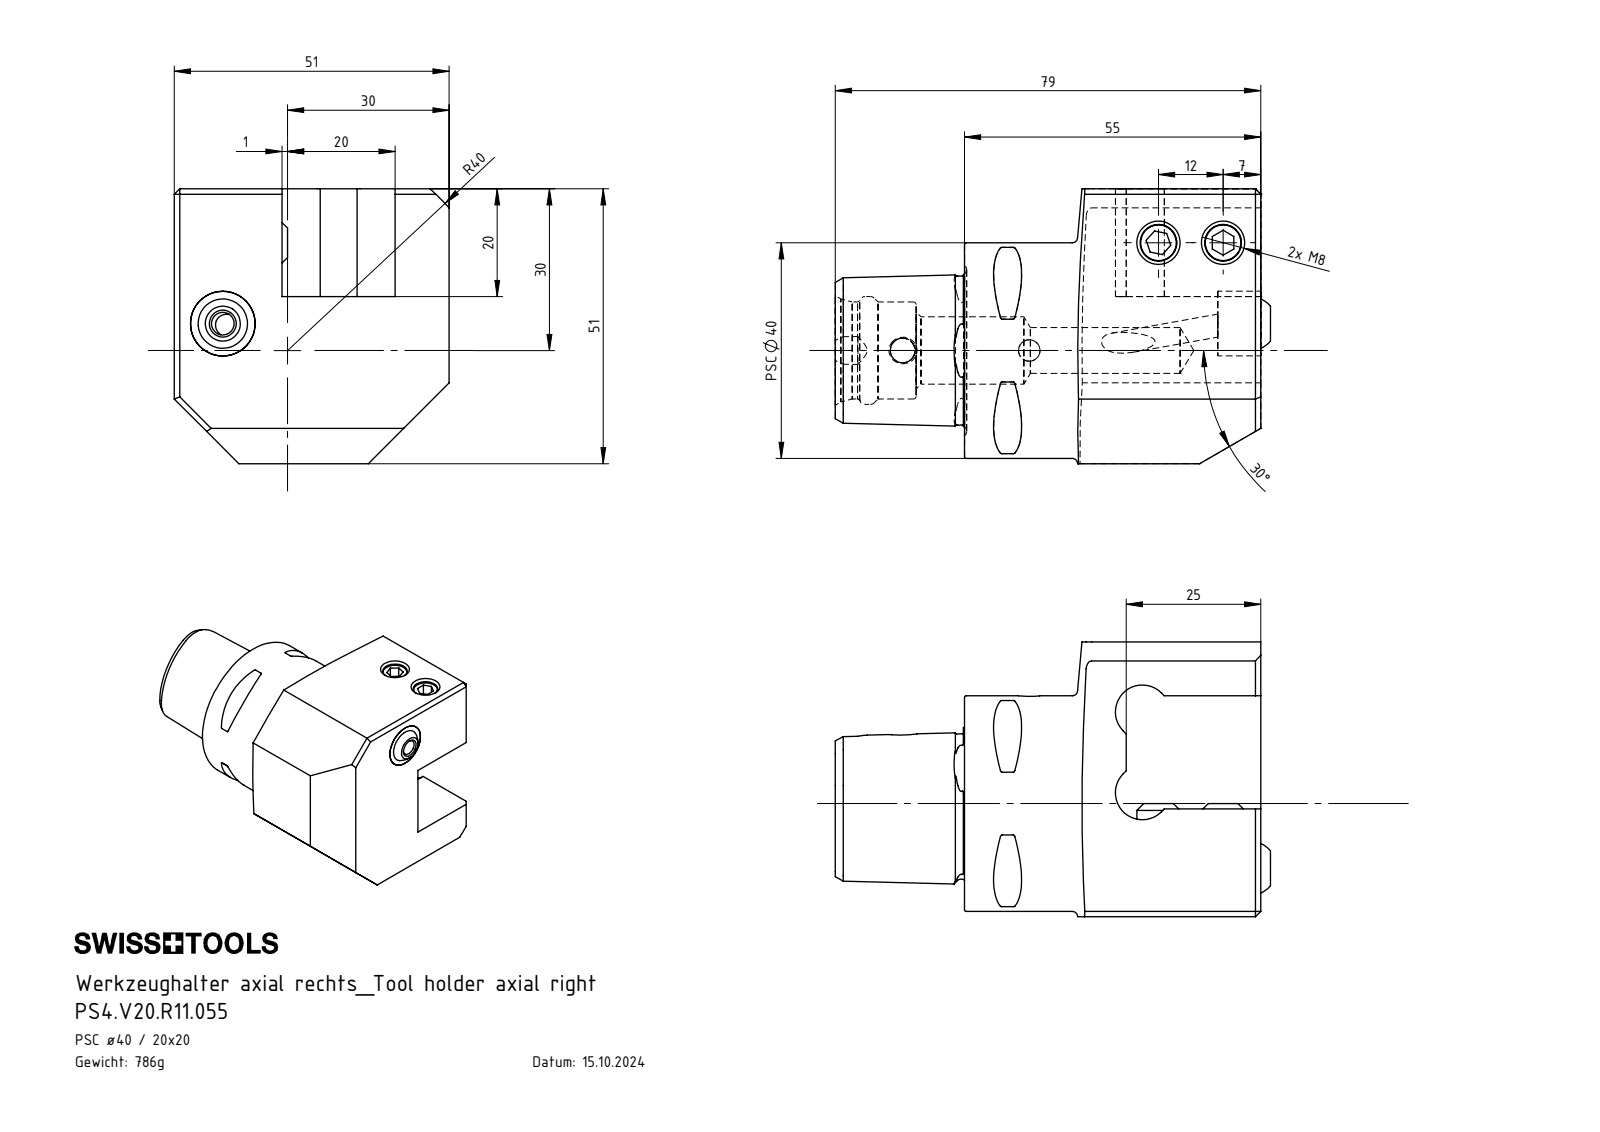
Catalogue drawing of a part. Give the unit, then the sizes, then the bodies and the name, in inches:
Units: inches
Overall size (bounding box): 3.181 × 2.008 × 2.008
Round holes (diameter × count): ⌀0.165 ×2, ⌀0.268 ×2, ⌀0.157 ×1, ⌀0.181 ×1, ⌀0.276 ×1, ⌀0.335 ×1, ⌀0.472 ×1, ⌀0.492 ×1, ⌀0.709 ×1, ⌀0.787 ×1
Round bosses / shafts (diameter × count): ⌀0.315 ×2, ⌀1.575 ×1
Partial cylindrical surfaces — rounded edges, fillets, slot ends (radius × count): R0.012 ×8, R0.197 ×2, R0.118 ×1, R1.575 ×1
Main face-to-face distances: 2.008, 0.787, 1.22, 2.165, 0.394, 0.827, 1.614, 1.181, 1.85, 0.315
Hole centre spacings: 0.472, 0.512, 0.925, 1.23, 1.621, 2.029, 2.471
Volume: 6.127 in³ · Surface area: 34.95 in²
Bodies: 5 solids, 219 faces (63 planar, 49 cylindrical, 107 other)
Part name (STEP PRODUCT): PS4-V20.R11.055_A; KU1-U12.001.010_1; ISO 4026 - M8 x 20; PS4.V20.R11.055 (+2 more)
STEP written by: SolidWorks 2022 (AUTOMOTIVE_DESIGN)
